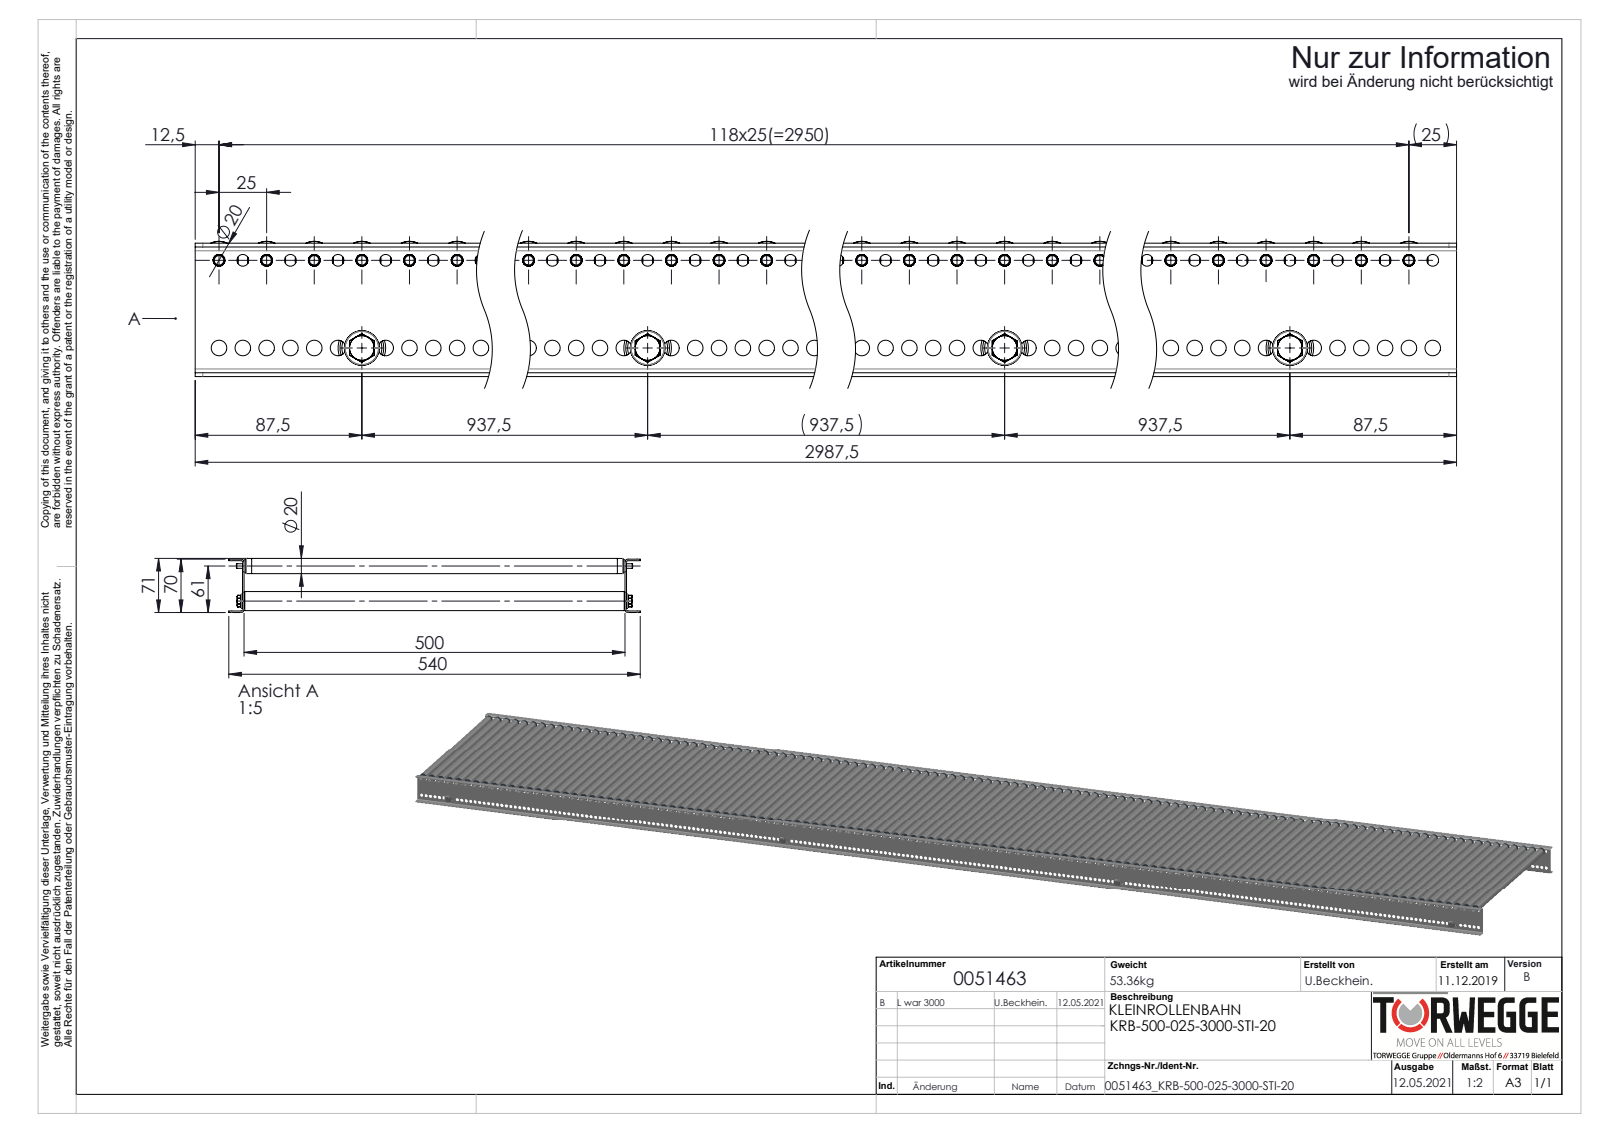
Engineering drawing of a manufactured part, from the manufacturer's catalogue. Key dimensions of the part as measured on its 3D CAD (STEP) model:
Part name (STEP PRODUCT): S100993_Tragrollenrohr-Ø20x1STI_KFG_L=480; Traversen_KFG_L500; KUT50-20x1,5-STI-A6_FA-EL=KFG_S100911_KUT50-20x1-STI-A6-FA-EL=500; Profil_KRB-20x70x20x2_KFG_S109089_U-PROFIL-20-70-20-2-KRB-20-L=2987,5 (+4 more)
STEP written by: SolidWorks 2020 (AUTOMOTIVE_DESIGN)
Units: millimetres
Bodies: 260 solids, 23356 faces (7582 planar, 8902 cylindrical, 6872 other)
Overall size (bounding box): 2987.5 × 540 × 71
Volume: 6 661 000 mm³ · Surface area: 10 300 000 mm²
Round holes (diameter × count): ⌀6.2 ×238, ⌀8.2 ×238, ⌀6.1 ×119, ⌀14.2 ×119, ⌀17.2 ×119, ⌀18 ×119, ⌀6.8 ×4, ⌀21 ×4
Round bosses / shafts (diameter × count): ⌀20 ×119, ⌀19.9 ×119, ⌀18.1 ×119, ⌀17.8 ×119, ⌀16.5 ×119, ⌀6 ×119, ⌀25 ×4, ⌀8 ×4
Partial cylindrical surfaces — rounded edges, fillets, slot ends (radius × count): R4.05 ×119, R4 ×8, R2 ×4
Main face-to-face distances: 2, 502, 68, 500, 504, 70, 66, 492, 18, 30
Hole centre spacings: 12.5, 25, 37.5, 50, 62.5, 75, 87.5, 100
